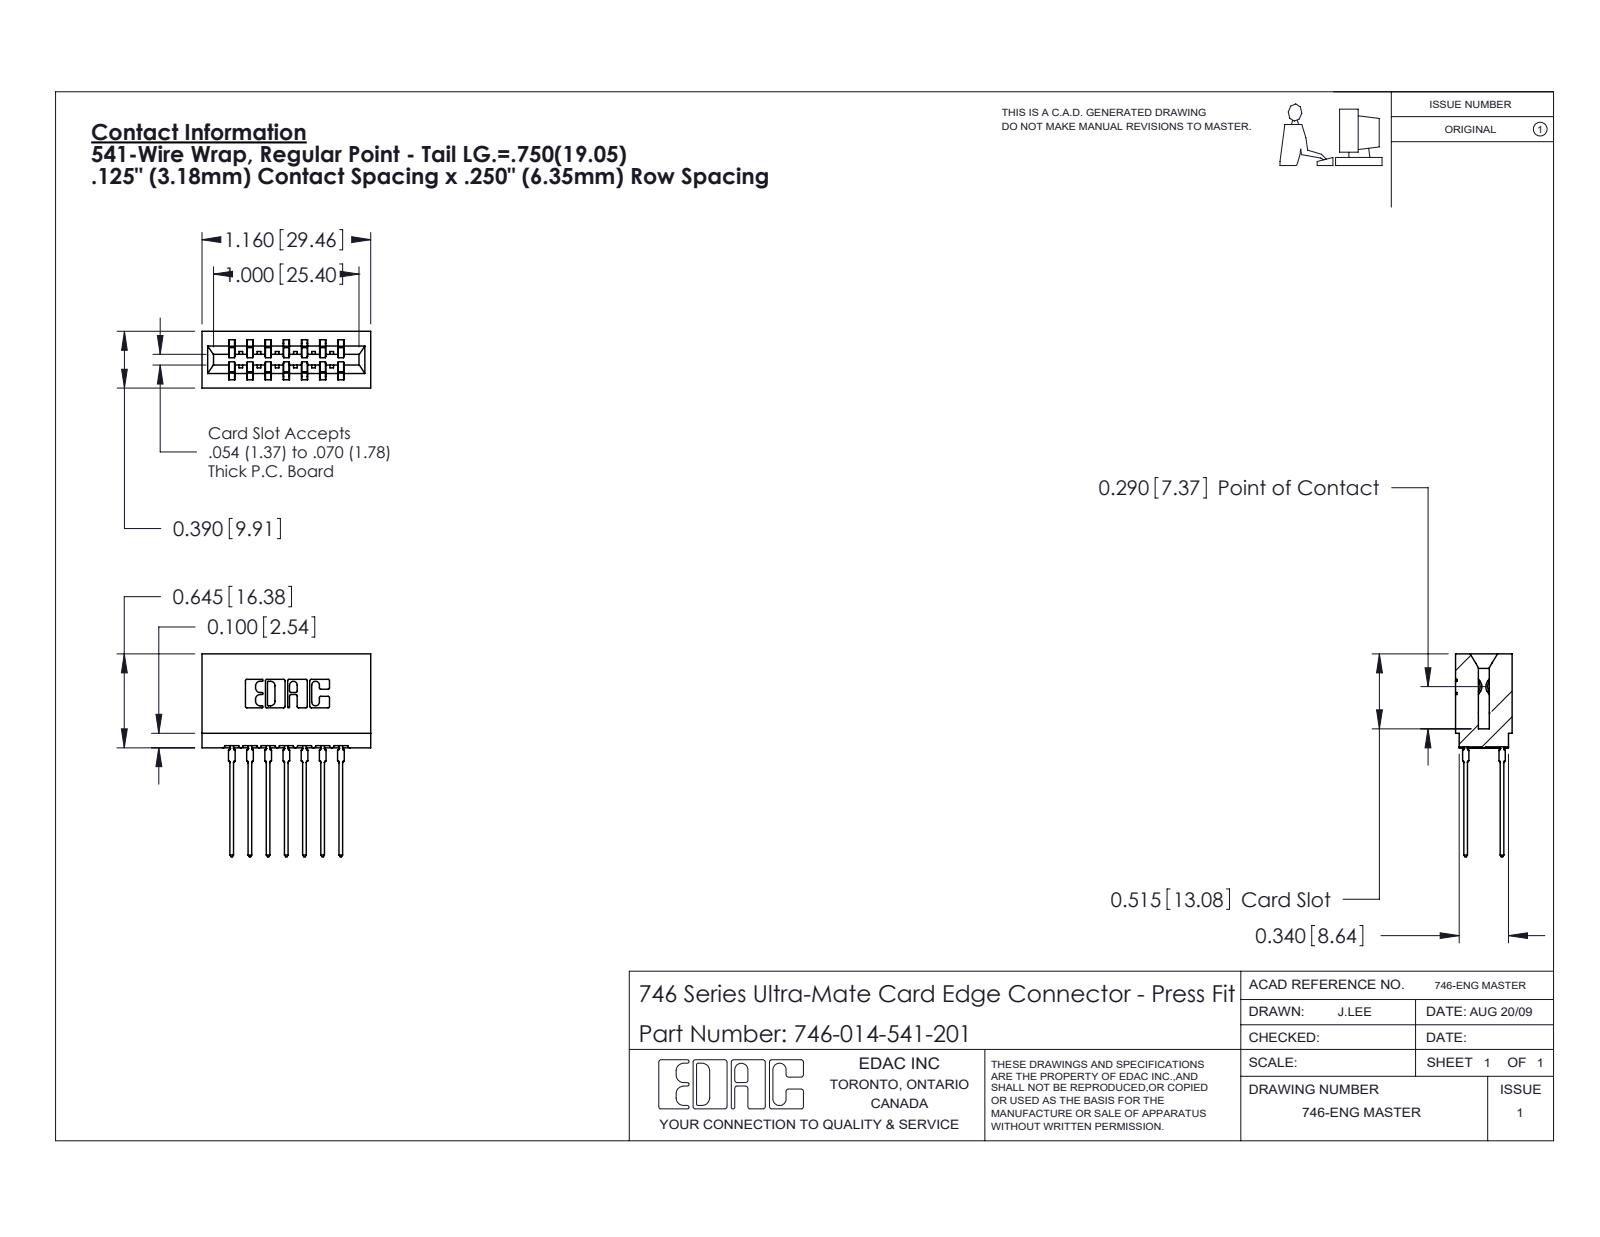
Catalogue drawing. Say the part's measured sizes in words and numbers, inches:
The part is named "746-014-541-201; 746-292-001_541; 746 Part_.515 Slot Depth - 01". Its 3-D file was written by "SolidWorks 2020 (CONFIG_CONTROL_DESIGN)". It is 15 solids with 1350 faces: 699 planar, 287 cylindrical and 364 other. Overall it measures 1.394 by 1.16 by 0.39 inches. Its volume is 0.211 cubic inches and its surface area 8.081 square inches. Partial cylindrical surfaces (rounded edges, fillets, slot ends): 28 of radius 0.021, 22 of radius 0.01, 8 of radius 0.005, 8 of radius 0.011, 8 of radius 0.015, 6 of radius 0.007, 6 of radius 0.031, 3 of radius 0.026. The main face-to-face distances are 0.25, 0.333, 0.057, 0.042, 0.125, 0.125, 0.083, 0.5, 0.025, 0.292.
